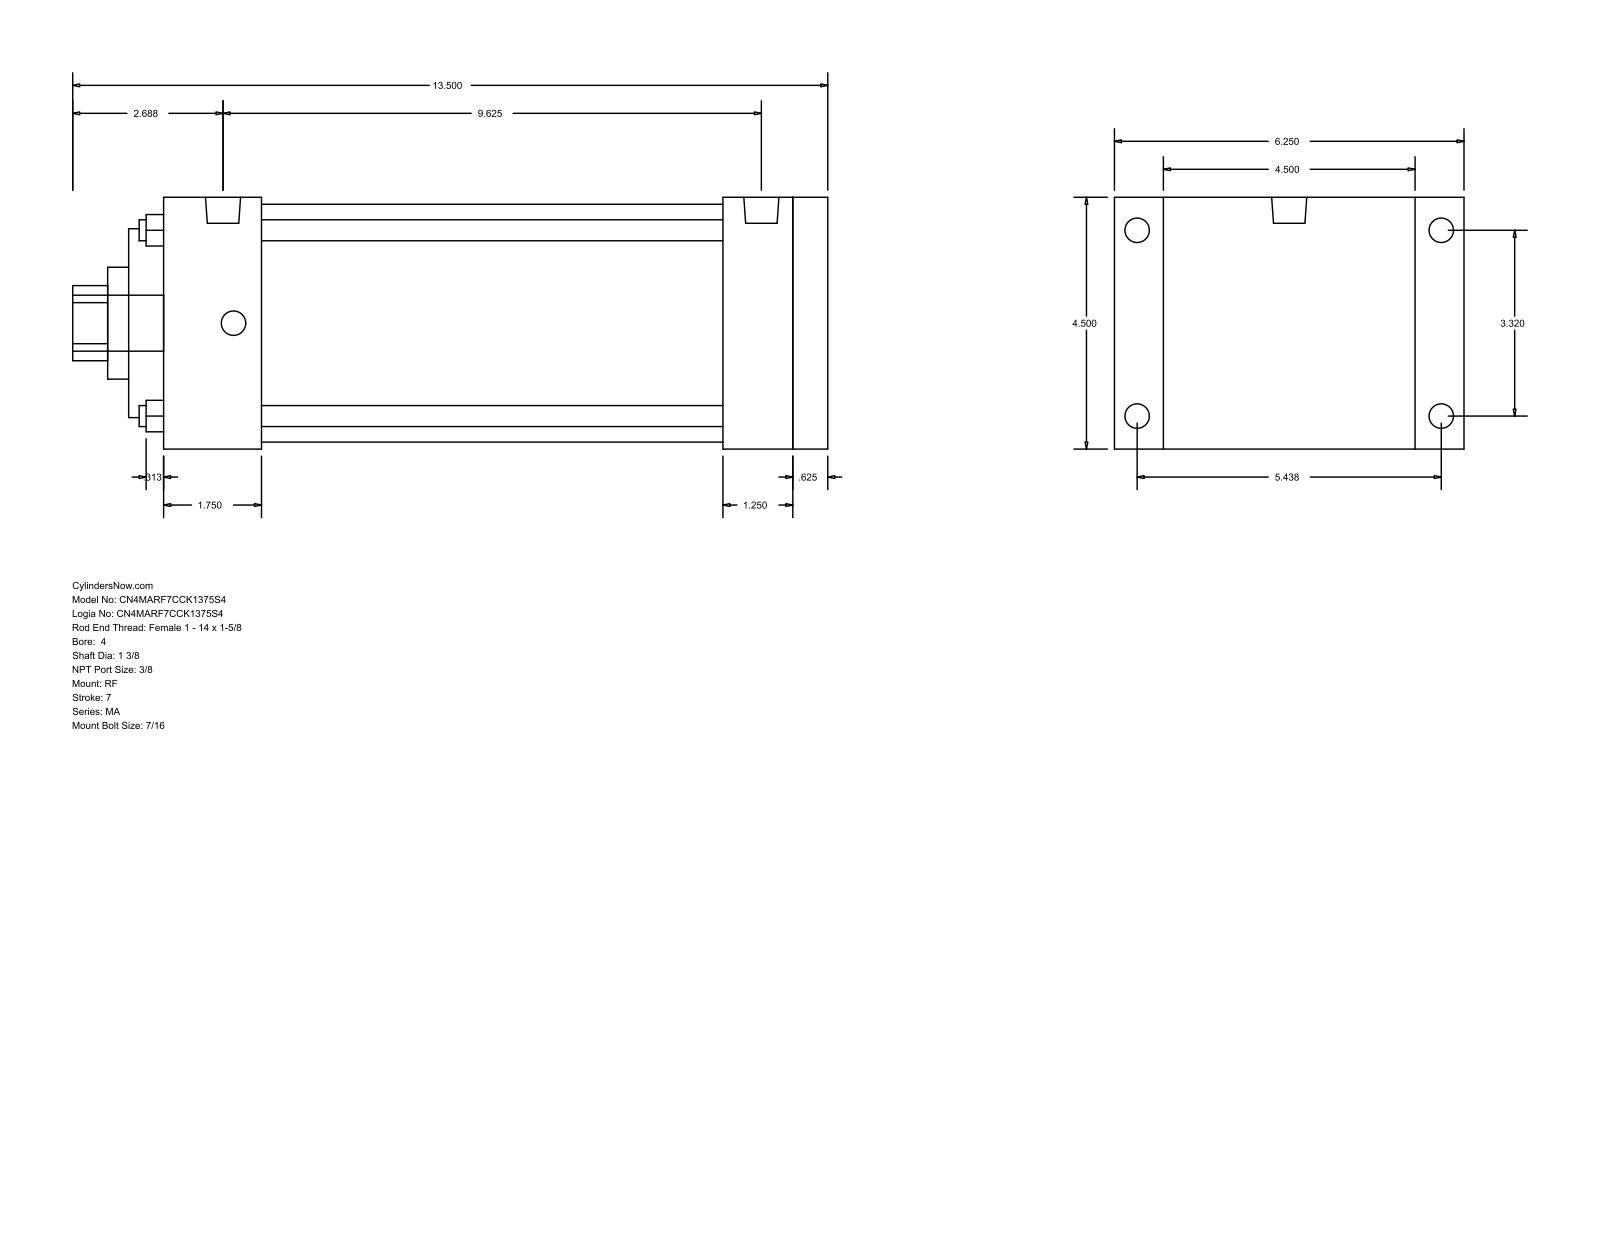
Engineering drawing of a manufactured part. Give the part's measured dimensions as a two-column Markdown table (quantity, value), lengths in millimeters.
| quantity | value |
| --- | --- |
| part name | MA_RF__0400_1.375 |
| STEP written by | GSSL Pune (CONFIG_CONTROL_DESIGN) |
| units | millimeters |
| bodies | 0 solids, 94 faces (65 planar, 29 cylindrical, 0 other) |
| overall size | 342.9 × 158.75 × 114.3 |
| round holes (diameter × count) | 9.53 × 4, 34.92 × 1, 50.8 × 1, 85.72 × 1, 107.95 × 1 |
| round bosses / shafts (diameter × count) | 11.11 × 8, 15.93 × 2, 25.4 × 1 |
| partial cylindrical surfaces (radius × count) | 17.06 × 1 |
| main face-to-face distances | 114.3, 301.63, 15.88, 285.75, 15.87, 301.62, 317.5, 22.23, 136.53, 269.87 |
| hole center spacings | 59.62, 84.32, 119.25 |
